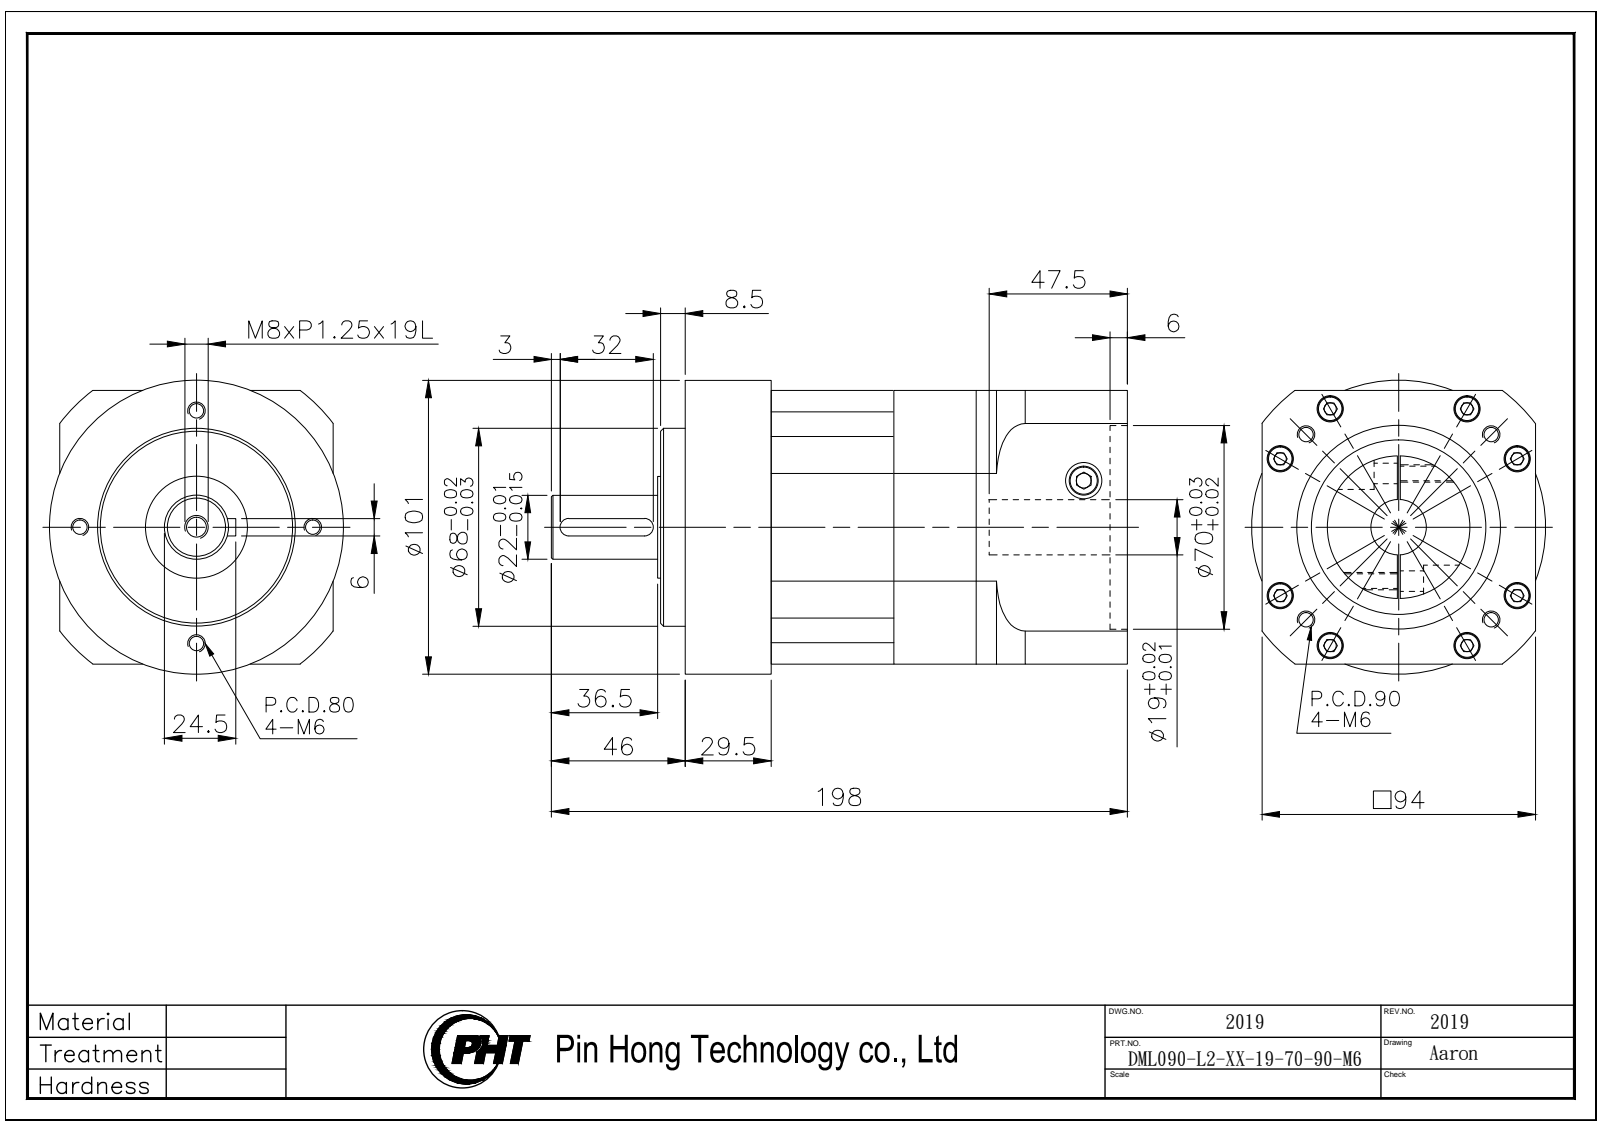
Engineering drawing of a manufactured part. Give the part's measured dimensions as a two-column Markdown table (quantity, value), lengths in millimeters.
| quantity | value |
| --- | --- |
| part name | DML090-L2-XX-19-70-90-M6_2019 |
| STEP written by | SolidWorks 2016 (AUTOMOTIVE_DESIGN) |
| units | millimeters |
| bodies | 4 solids, 271 faces (114 planar, 117 cylindrical, 40 other) |
| overall size | 198 × 101 × 101 |
| volume | 1 147 000 mm³ |
| surface area | 152 409 mm² |
| round holes (diameter × count) | 5 × 8, 5.2 × 8, 9 × 8, 12.7 × 2, 6.8 × 1, 19 × 1, 60 × 1, 70 × 1 |
| round bosses / shafts (diameter × count) | 8.5 × 8, 101 × 1, 68 × 1, 49 × 1, 35 × 1, 22 × 1 |
| partial cylindrical surfaces (radius × count) | 6 × 4, 3 × 2, 59 × 1 |
| main face-to-face distances | 70.5, 28.3, 42.2, 94, 100, 71.7, 29.5, 52, 80.3, 122.5 |
| hole center spacings | 47, 12.17, 23.51, 32.85, 43.92, 56.03, 66.46, 73 |
